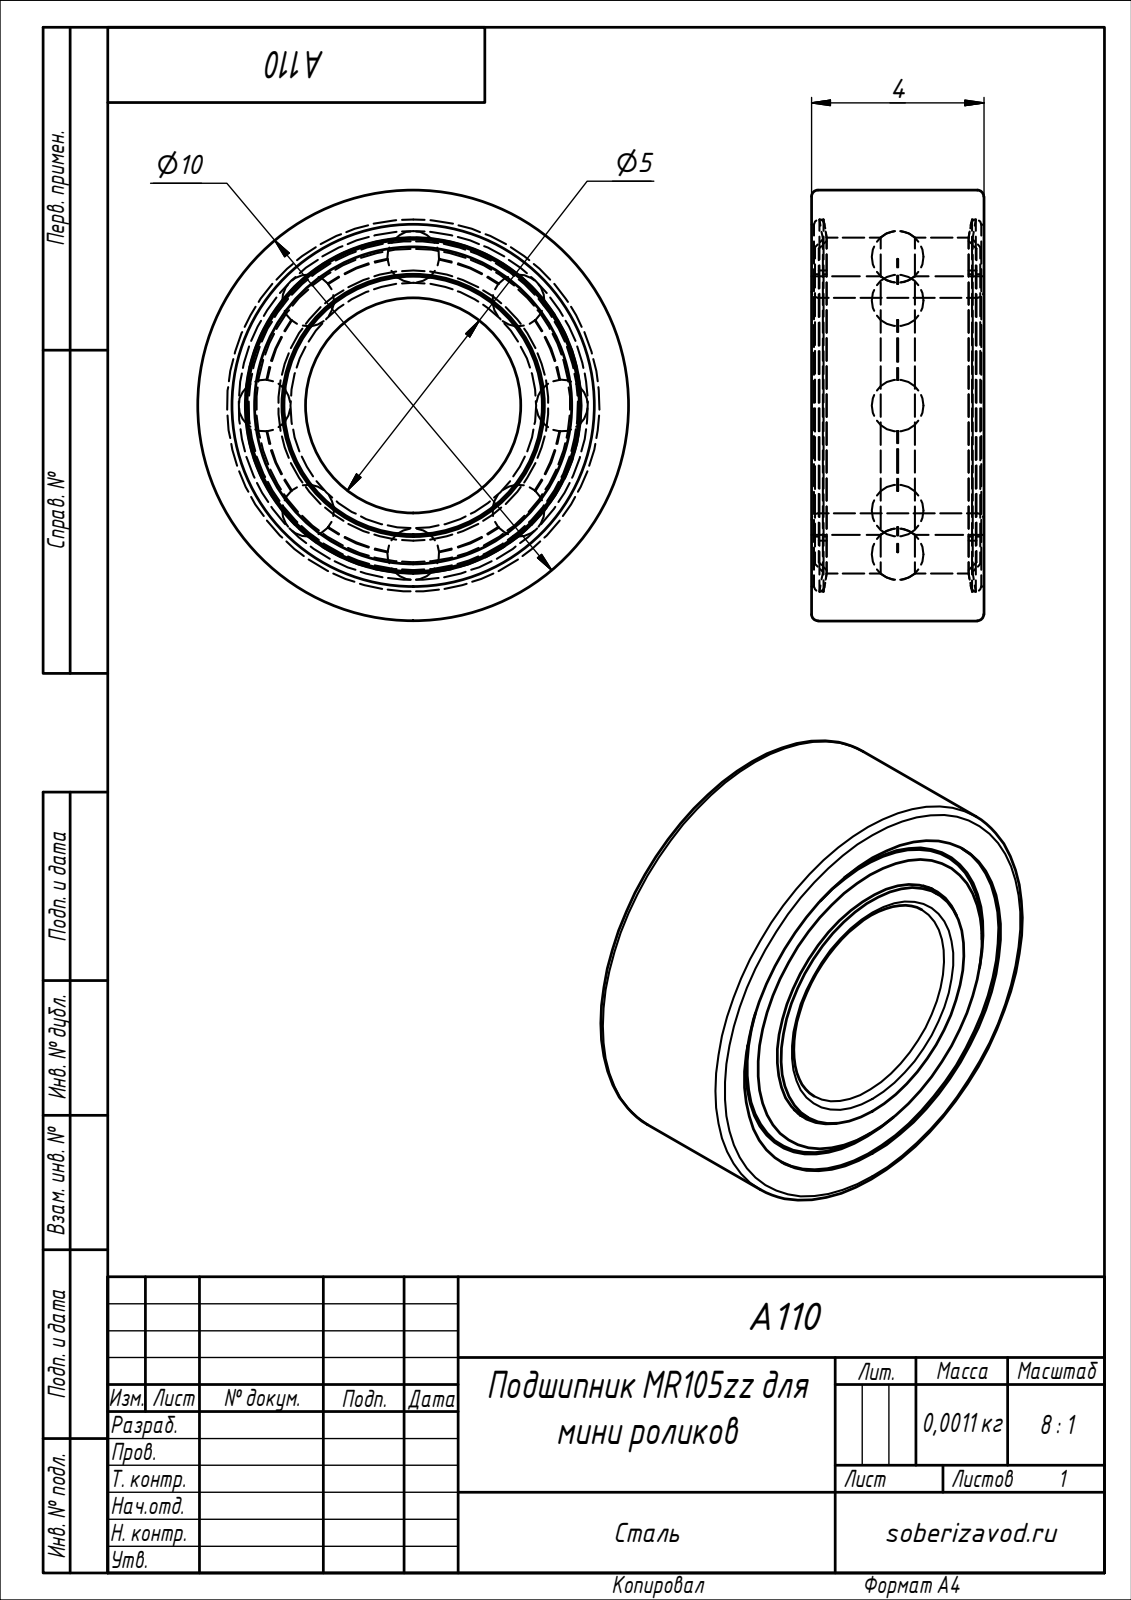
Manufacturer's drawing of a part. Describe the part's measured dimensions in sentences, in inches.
The part is named "A110; roulement_wbb1-8705-2z_2_01; roulement_wbb1-8705-2z_2_02; roulement_wbb1-8705-2z_2_03 (+2 more)". Its 3-D file was written by "Autodesk Inventor 2018 (AP242_MANAGED_MODEL_BASED_3D_ENGINEERING_MIM_LF)". It is 5 solids with 62 faces: 14 planar, 14 cylindrical and 34 other. Overall it measures 0.394 by 0.394 by 0.157 inches. Its volume is 0.01 cubic inches and its surface area 0.975 square inches. Round holes: 1 of diameter 0.197, 1 of diameter 0.24, 1 of diameter 0.307, 1 of diameter 0.331. Round bosses or shafts: 1 of diameter 0.394, 1 of diameter 0.34, 1 of diameter 0.247, 1 of diameter 0.236. The main face-to-face distances are 0.154, 0.157, 0.151, 0.148, 0.151, 0.144, 0.141, 0.137, 0.014, 0.144.
